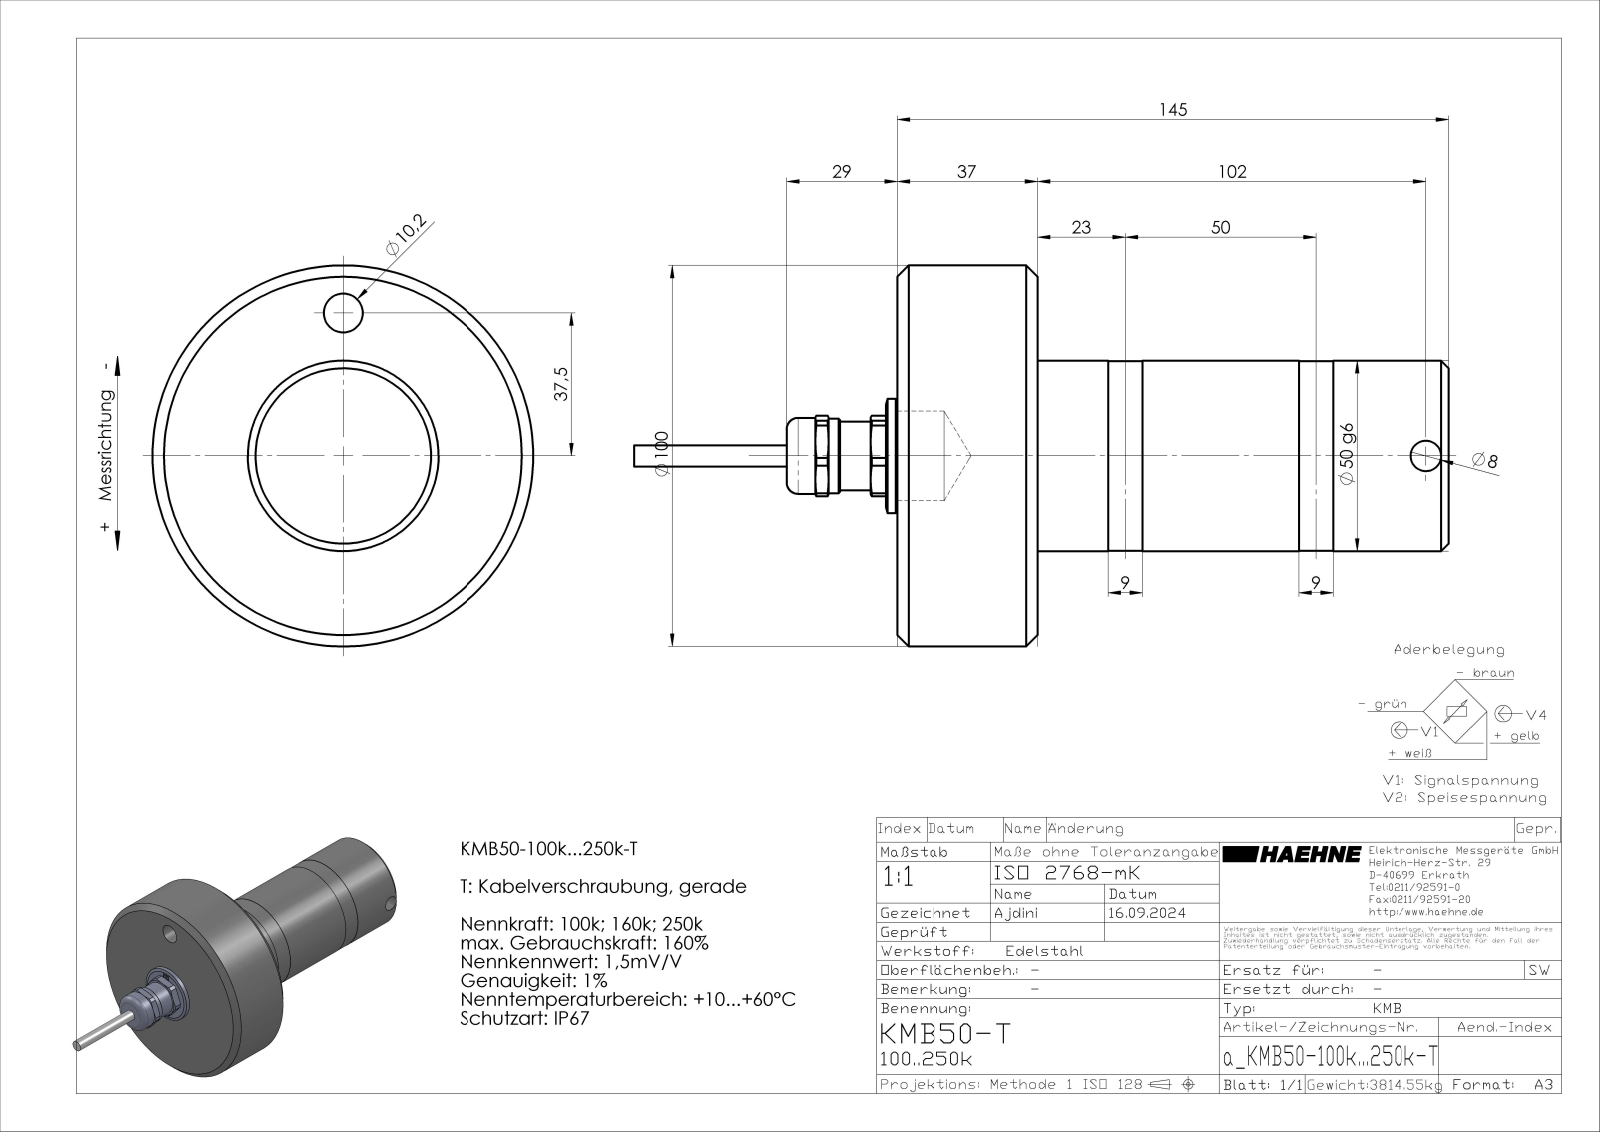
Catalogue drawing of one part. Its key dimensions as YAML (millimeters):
part_name: "a_KMB50-100k...150k-T_Angebot; Kabel; a_KMB50-100k...250k-T; X02045Z1 SKINDICHT MR-M 25x1,5 _ 16x1,5 Art_ Nr_ 52104313 (+1 more)"
step_written_by: "SolidWorks 2023 (CONFIG_CONTROL_DESIGN)"
units: millimeters
bodies: {solids: 4, faces: 147, planar: 63, cylindrical: 53, other: 31}
overall_size: [214, 100, 100]
volume: 500721
surface_area: 52592
round_holes:
  - {diameter: 0.89, count: 5}
  - {diameter: 1.22, count: 5}
  - {diameter: 4.5, count: 1}
  - {diameter: 8, count: 1}
  - {diameter: 10.2, count: 1}
  - {diameter: 23.5, count: 1}
round_bosses_or_shafts:
  - {diameter: 100, count: 1}
  - {diameter: 50, count: 1}
  - {diameter: 49.8, count: 1}
  - {diameter: 30, count: 1}
  - {diameter: 25, count: 1}
  - {diameter: 23.16, count: 1}
  - {diameter: 19.98, count: 1}
  - {diameter: 19.6, count: 1}
partial_cylinders:
  - {radius: 11, count: 1}
face_to_face_distances: [37, 108, 145, 3, 40, 148, 7, 33, 138, 30]
hole_center_spacings: [0.94, 1.52, 1.29, 2.09, 11.14, 27.65, 1.3, 2.1]
